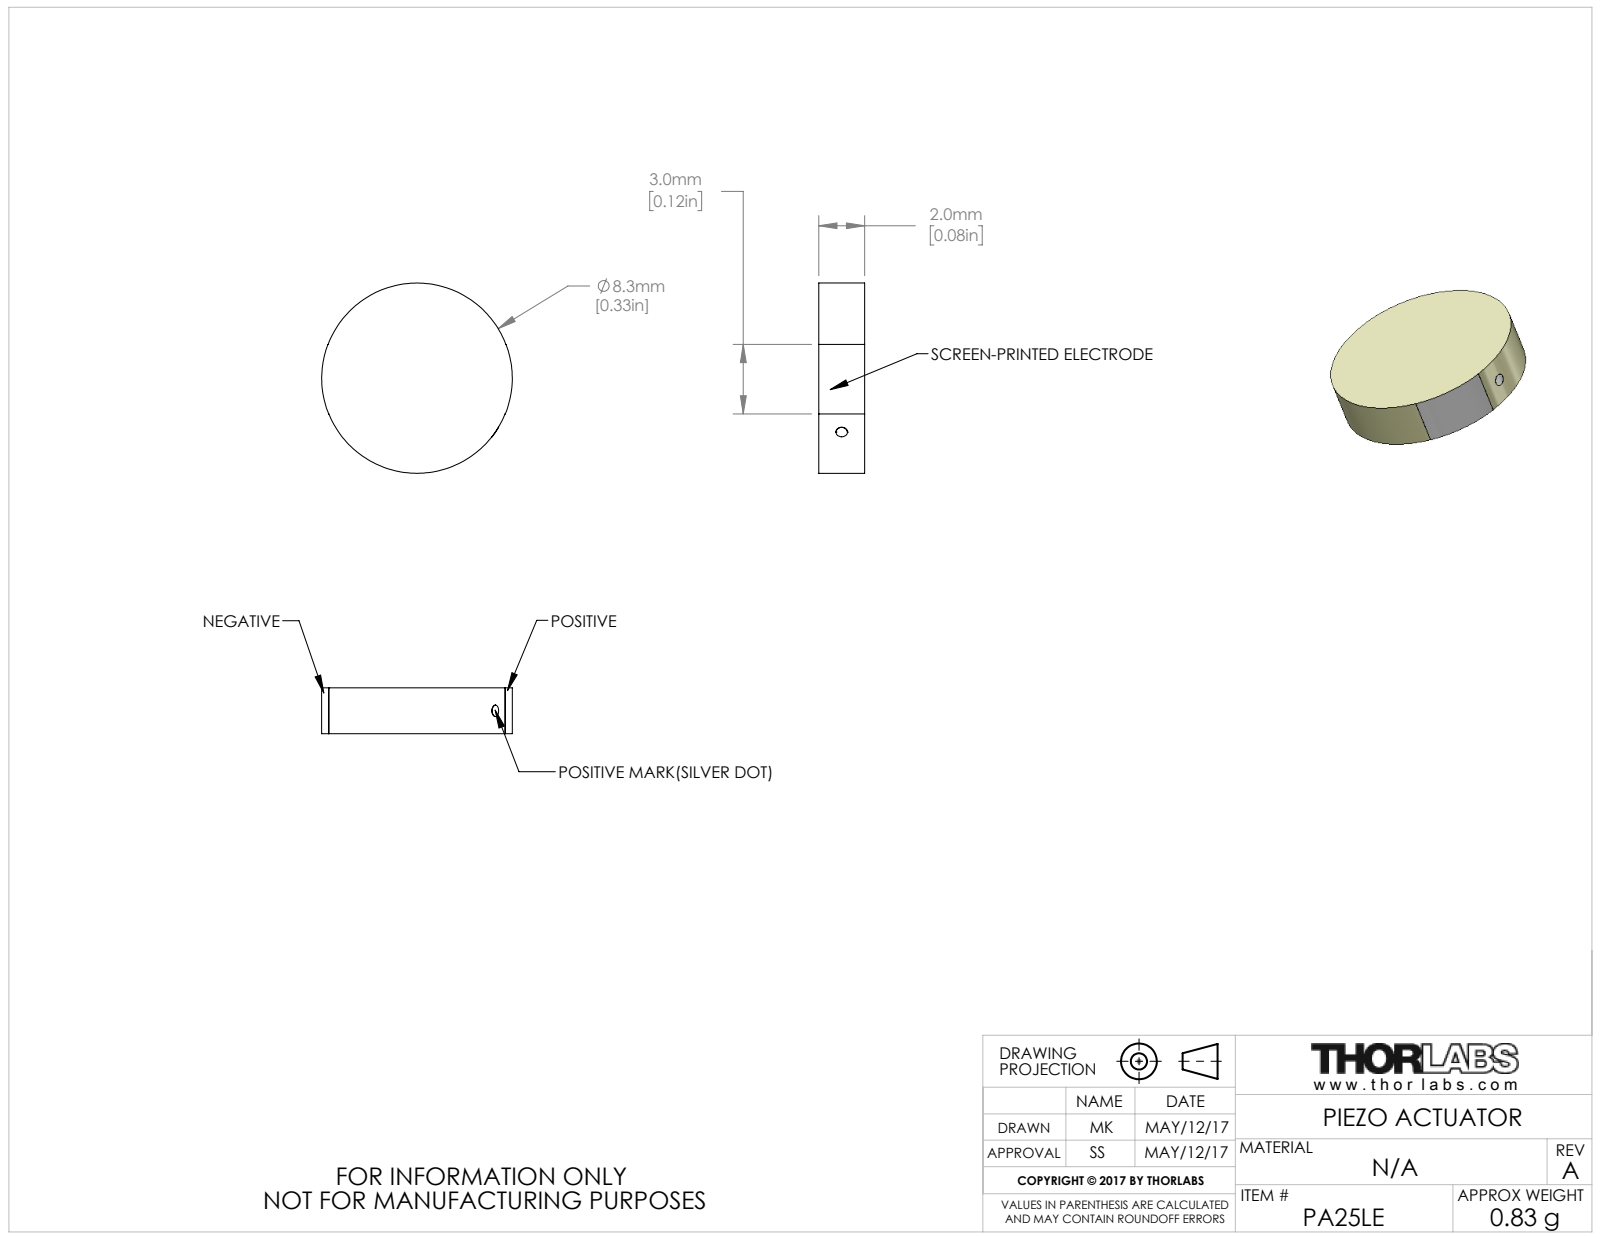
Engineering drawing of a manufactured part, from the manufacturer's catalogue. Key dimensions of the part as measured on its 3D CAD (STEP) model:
Part name (STEP PRODUCT): CTN010613
STEP written by: SolidWorks 2016 (AUTOMOTIVE_DESIGN)
Units: millimetres
Bodies: 1 solid, 14 faces (6 planar, 6 cylindrical, 2 other)
Overall size (bounding box): 8.32 × 8.3 × 2
Volume: 108 mm³ · Surface area: 161 mm²
Partial cylindrical surfaces — rounded edges, fillets, slot ends (radius × count): R4.15 ×1, R4.16 ×1
Main face-to-face distances: 2
